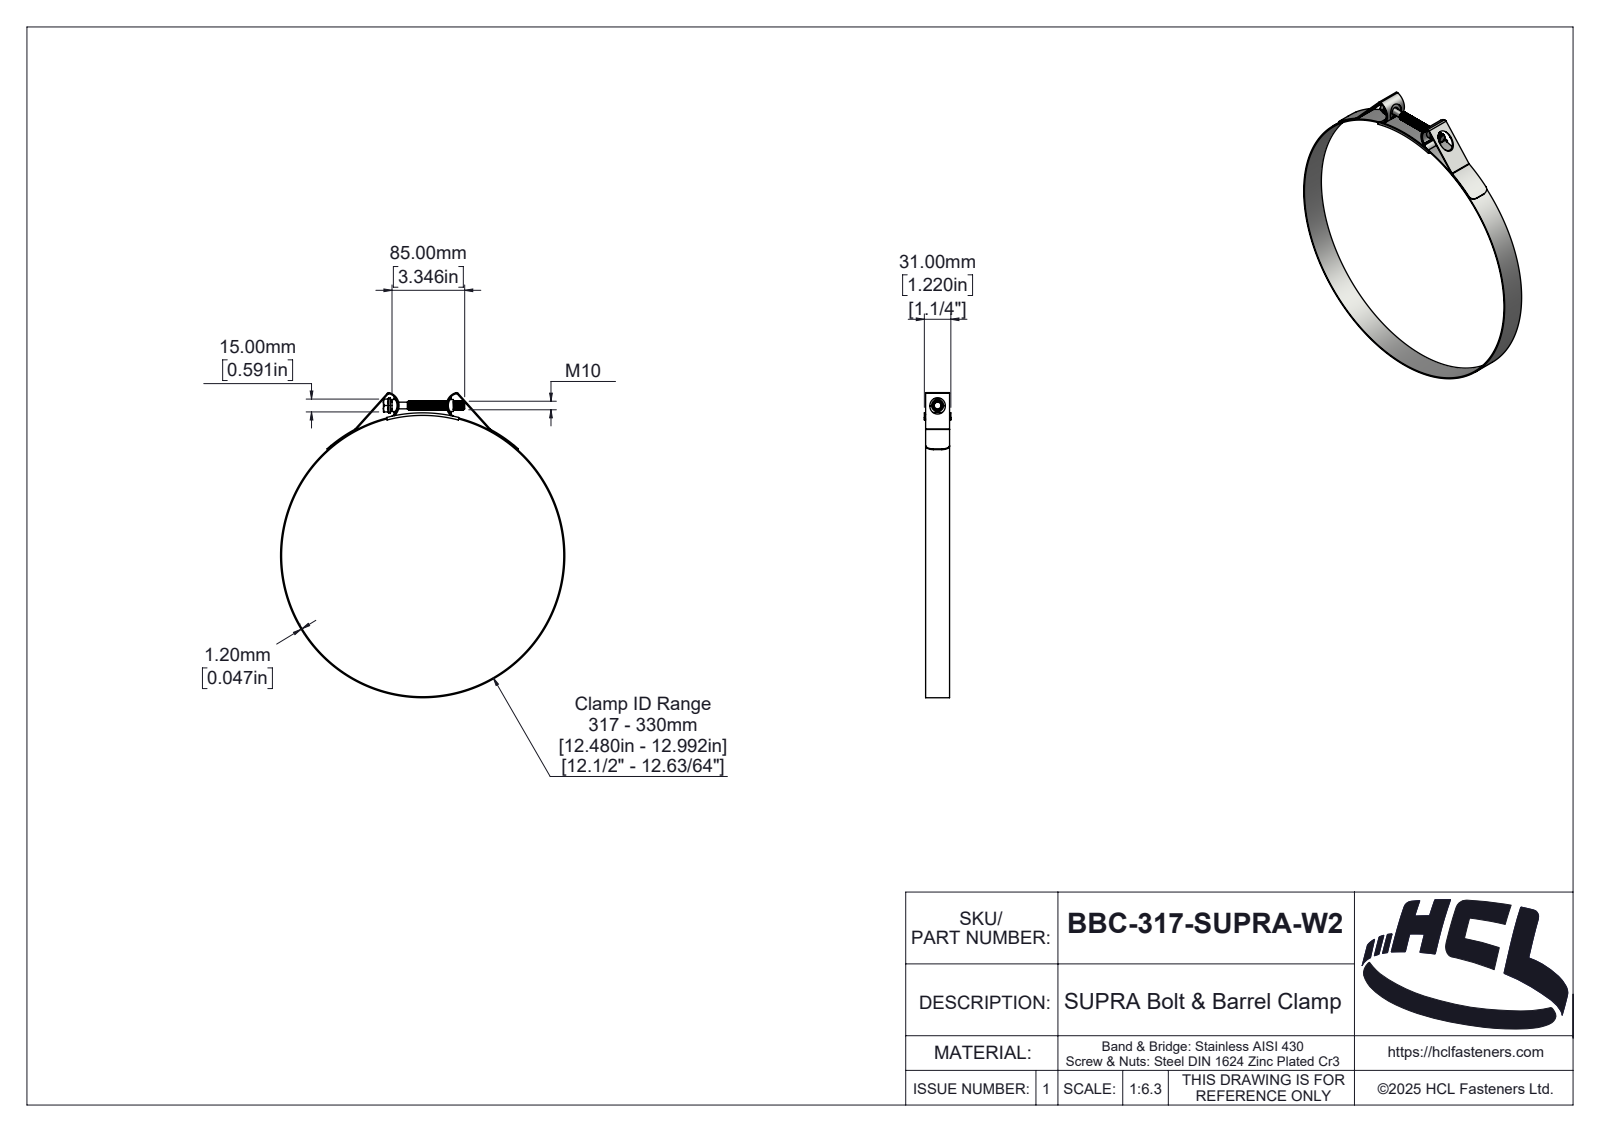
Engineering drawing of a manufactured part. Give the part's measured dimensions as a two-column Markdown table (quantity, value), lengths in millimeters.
| quantity | value |
| --- | --- |
| part name | BBC-317-SUPRA-W2 |
| STEP written by | SolidWorks 2025 (AUTOMOTIVE_DESIGN) |
| units | millimeters |
| bodies | 5 solids, 380 faces (50 planar, 243 cylindrical, 87 other) |
| overall size | 356.62 × 332.4 × 31 |
| volume | 52 760 mm³ |
| surface area | 83 714 mm² |
| round holes (diameter × count) | 330 × 1 |
| round bosses / shafts (diameter × count) | 332.4 × 1, 17.32 × 1, 14 × 1, 10 × 1, 7.8 × 1 |
| partial cylindrical surfaces (radius × count) | 1 × 4, 1.3 × 2, 2 × 2, 2.5 × 2, 3.2 × 2, 9 × 2, 13.31 × 2, 14.31 × 2 |
| main face-to-face distances | 1.2, 28, 1.5, 29.5, 29.8, 28.3, 31, 28.6, 15, 2.5 |
